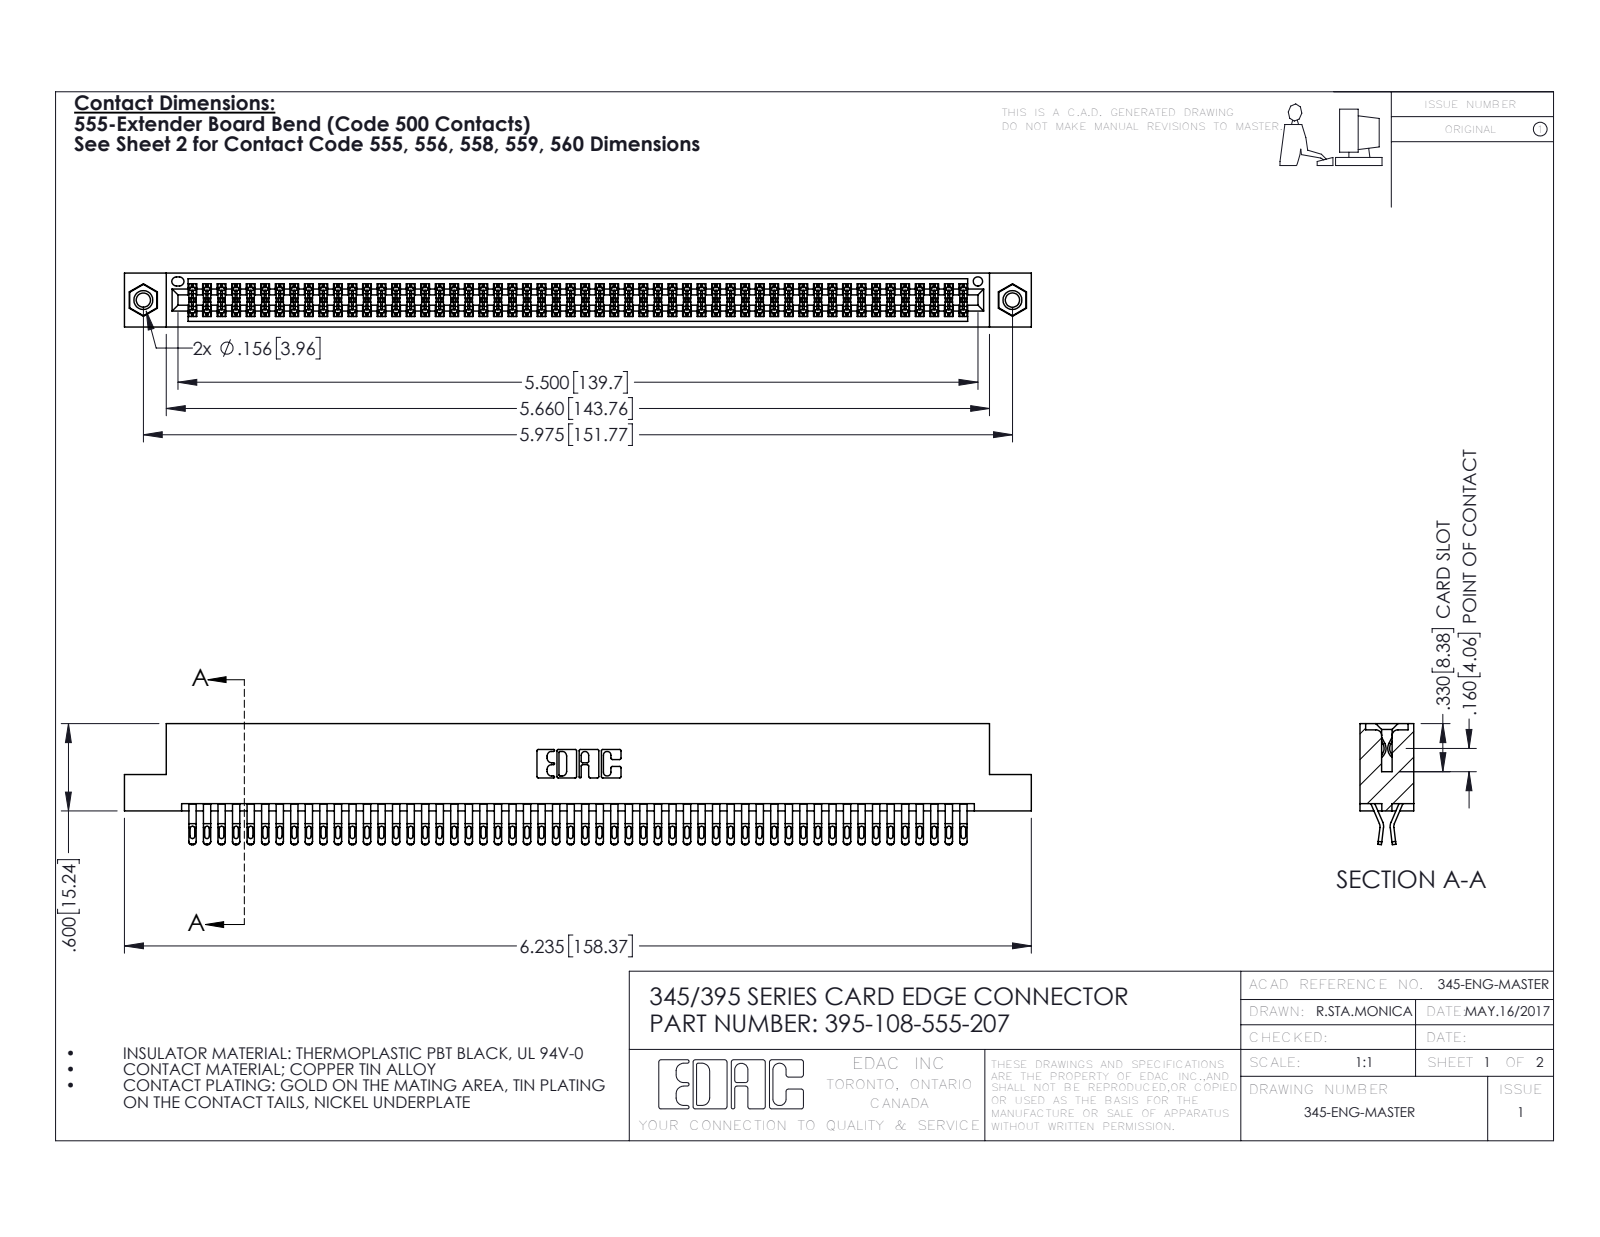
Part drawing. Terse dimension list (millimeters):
name: 345 Part_Flush Mounting Lugs - 0.156 Dia-TI; 345-292-001_555 Tail; 345-250-001_345-250-005-103; 395-108-555-207
written by: SolidWorks 2016 (CONFIG_CONTROL_DESIGN)
unit: mm
bodies: 111 solids, 6234 faces (3460 planar, 2758 cylindrical, 16 other)
size: 158.4 × 21.1 × 9.4
volume: 15 800 mm³; area: 24 700 mm²
holes: 2× ⌀2.5, 2× ⌀3.2, 2× ⌀4, 1× ⌀1.6
bosses: 2× ⌀3.9
rounds: 270× R0.4, 216× R0.5, 162× R0.2, 22× R0.3, 6× R0.2, 6× R0.8, 3× R0.7, 2× R0.3
face distances: 1.8, 7.6, 0.6, 9.4, 5.1, 2.5, 6.9, 5.7, 4.4, 3.8
hole spacings: 6.9, 145.8, 151.8
